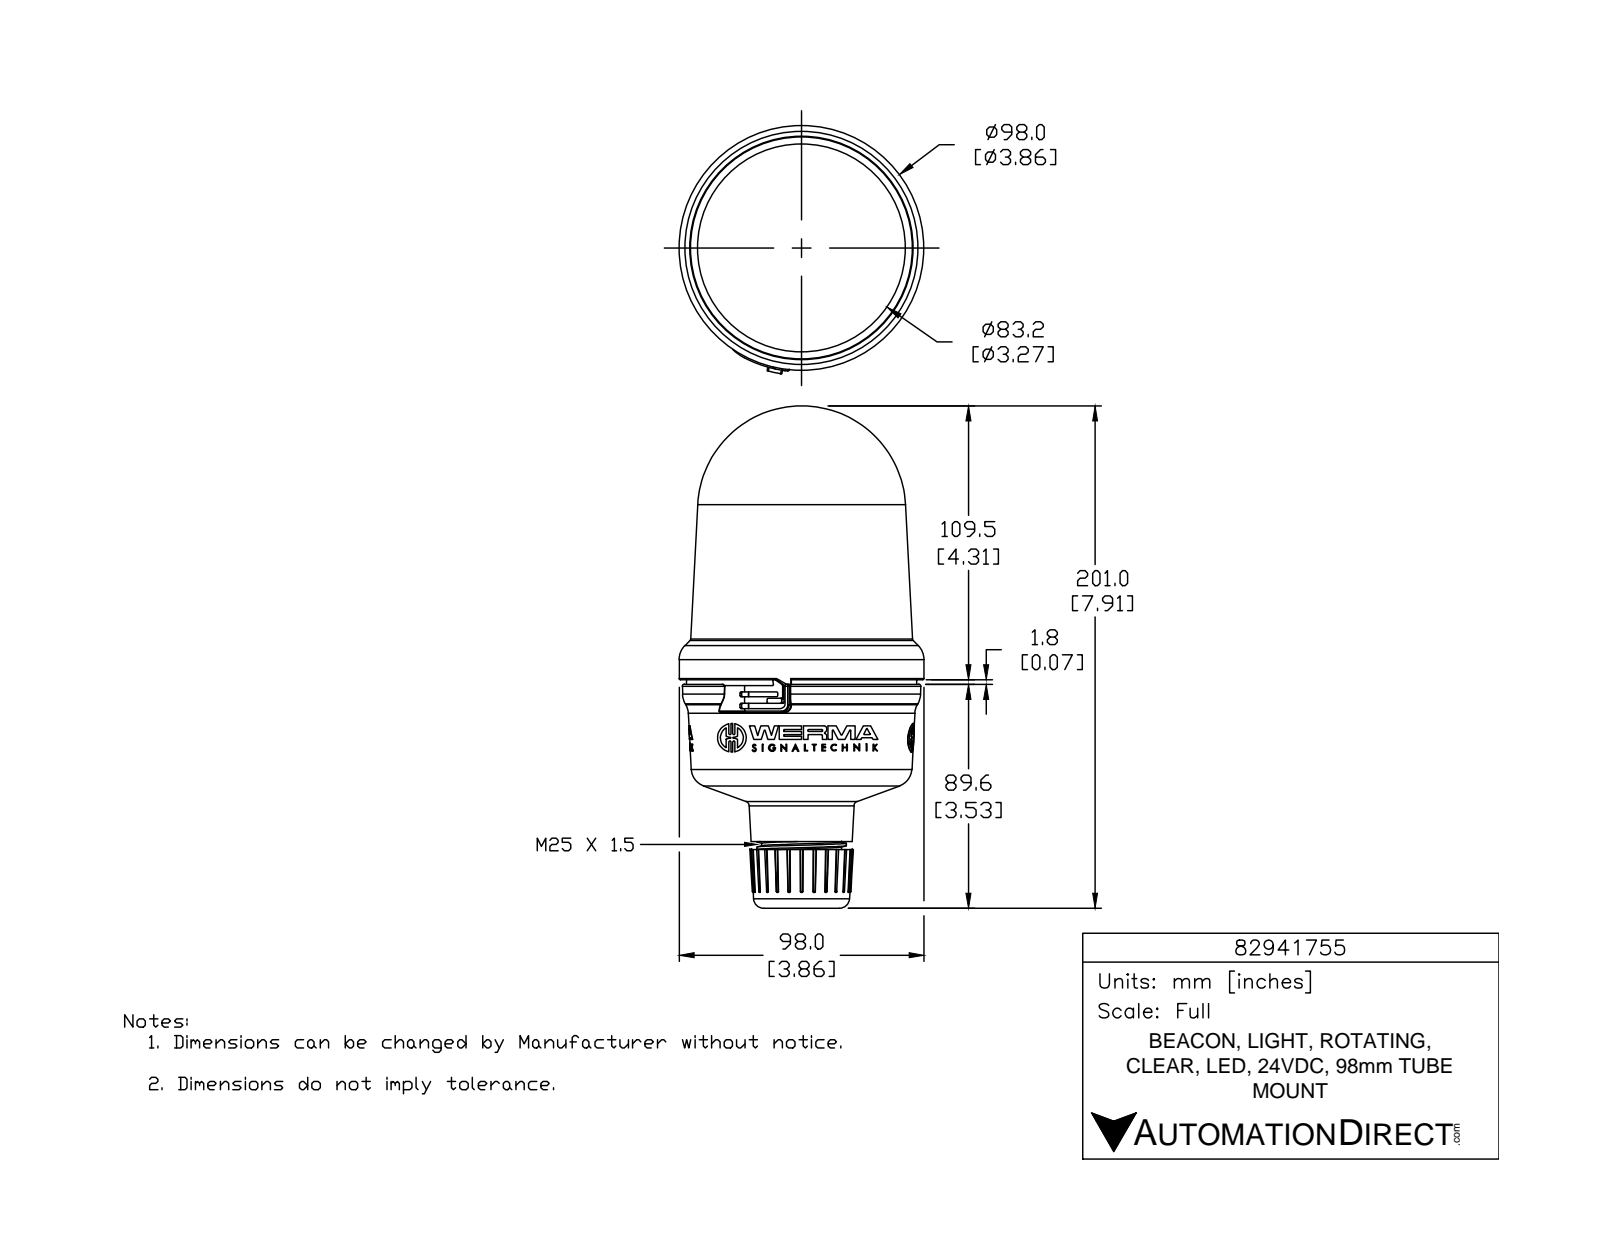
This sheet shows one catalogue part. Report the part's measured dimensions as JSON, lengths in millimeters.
{"part_name": "82941755", "step_written_by": "SolidWorks 2015 (AUTOMOTIVE_DESIGN)", "units": "millimeters", "bodies": {"solids": 1, "faces": 1006, "planar": 554, "cylindrical": 189, "other": 263}, "overall_size": [201, 99.4, 98], "volume_mm3": 896400, "surface_area_mm2": 58960, "round_holes": [[2, 3], [25.7, 1], [26, 1]], "round_bosses_or_shafts": [[11.5, 3], [2.9, 3], [98, 1], [35.8, 1], [32, 1]], "partial_cylinders_radius": [[0.5, 12], [0.2, 9], [0.2, 6], [0.4, 6], [0.4, 6], [0.4, 6], [6.7, 6], [0.2, 3]], "face_to_face_distances": [56.2, 11.7, 68, 8.5, 3.2, 64.7, 66.1, 62.9, 54.4, 1.9]}
